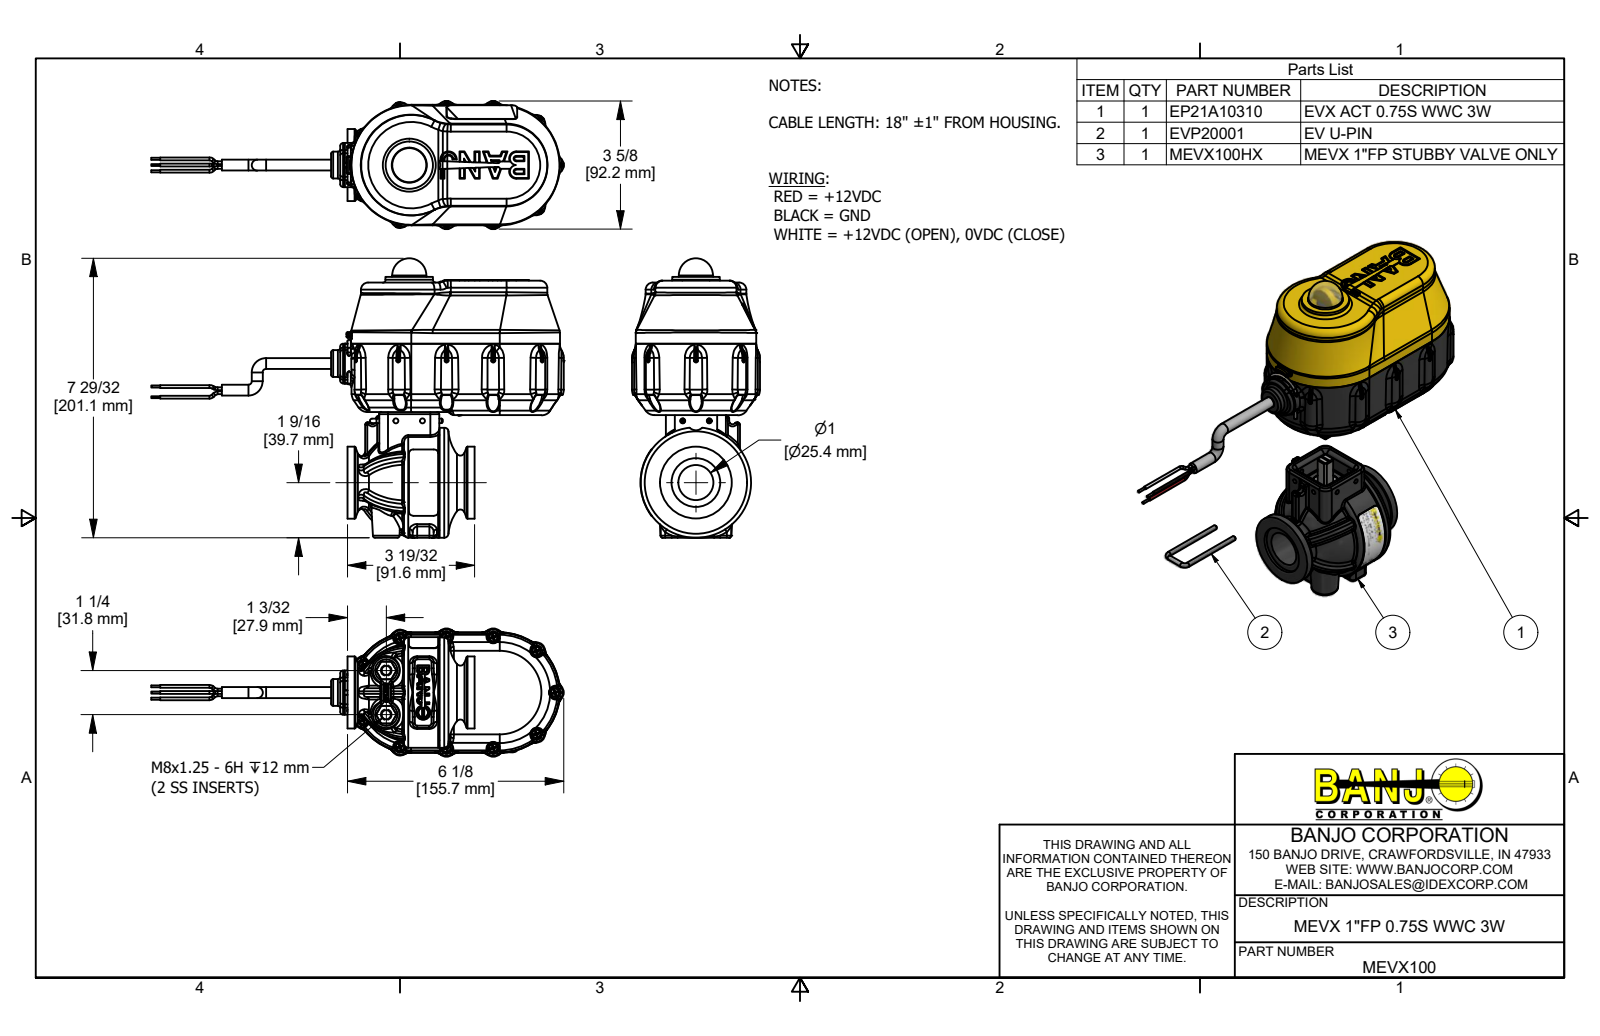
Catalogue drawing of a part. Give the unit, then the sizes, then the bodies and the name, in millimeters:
Units: millimetres
Overall size (bounding box): 296.8 × 201.1 × 92.2
Round holes (diameter × count): ⌀2.4 ×11, ⌀3.8 ×11, ⌀2 ×7, ⌀3.4 ×5, ⌀2.7 ×4, ⌀3.2 ×4, ⌀3.5 ×4, ⌀3.8 ×4, ⌀3.8 ×4, ⌀4.3 ×4, ⌀2.7 ×2, ⌀3 ×2
Round bosses / shafts (diameter × count): ⌀6.4 ×17, ⌀2 ×15, ⌀3.6 ×11, ⌀2.7 ×11, ⌀2.2 ×11, ⌀1.5 ×6, ⌀6.9 ×4, ⌀5.6 ×4
Partial cylindrical surfaces — rounded edges, fillets, slot ends (radius × count): R0.3 ×180, R1 ×145, R0.3 ×84, R0.5 ×71, R0.1 ×54, R1.5 ×46, R0.8 ×30, R2 ×28
Main face-to-face distances: 2.5, 65.2, 5.4, 1.5, 3.8, 48.2, 42.8, 46.6, 62.6, 19.8
Hole centre spacings: 45.5, 32.6, 67.5, 38.4, 42.2, 68.3, 72.4, 96.2
Volume: 760 900 mm³ · Surface area: 342 500 mm²
Bodies: 84 solids, 10960 faces (2986 planar, 3104 cylindrical, 4870 other)
Part name (STEP PRODUCT): MEVX100; EP21A10310; EP10310; IRF4905 (+8 more)
STEP written by: Autodesk Inventor 2019 (AUTOMOTIVE_DESIGN)
